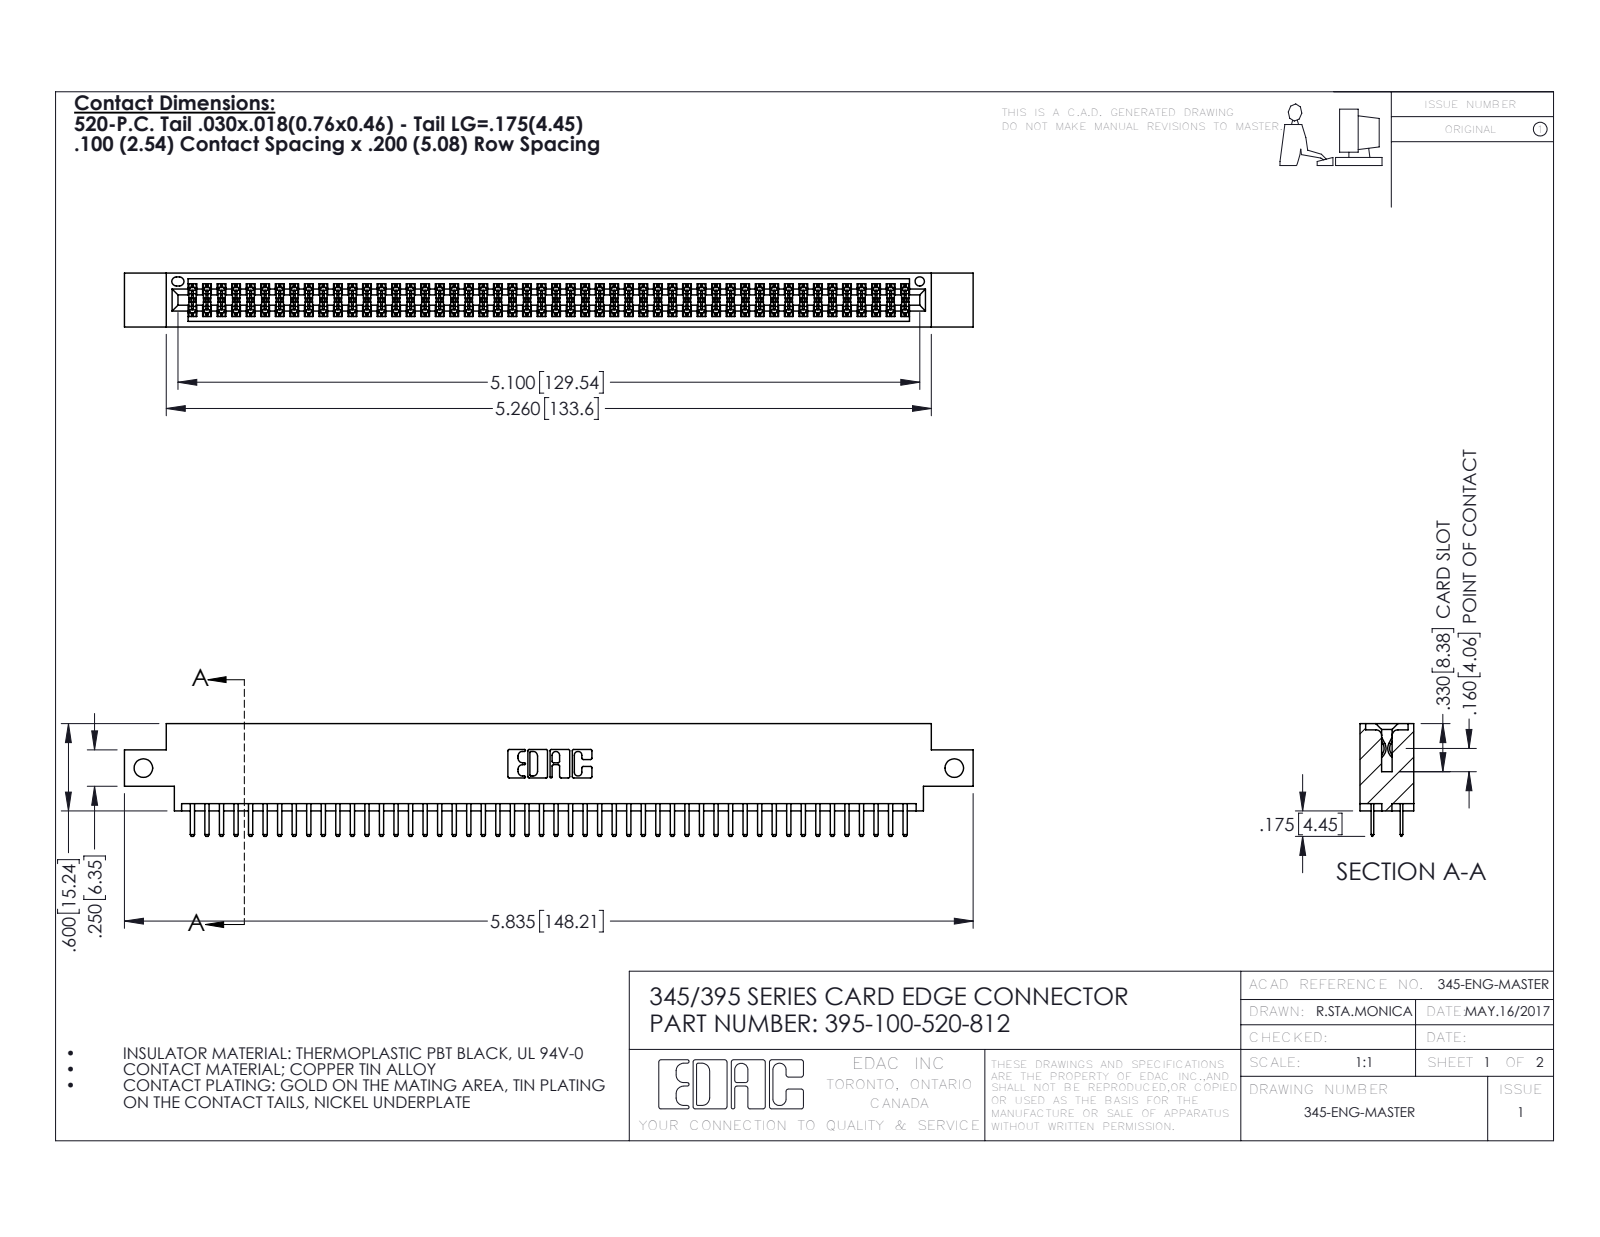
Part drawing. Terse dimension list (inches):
name: 395-100-520-812; 345-292-001_345-293-120; 345 Part_0.170 Offset - Side Mount
written by: SolidWorks 2016 (CONFIG_CONTROL_DESIGN)
unit: in
bodies: 101 solids, 5530 faces (3584 planar, 1946 cylindrical, 0 other)
size: 5.835 × 0.775 × 0.37
volume: 0.868 in³; area: 32.7 in²
holes: 2× ⌀0.128, 1× ⌀0.064
rounds: 150× R0.006, 104× R0.01, 22× R0.01, 6× R0.007, 6× R0.031, 3× R0.026, 2× R0.014, 2× R0.019
face distances: 0.072, 0.298, 0.2, 0.37, 0.098, 0.272, 0.025, 0.225, 0.022, 0.175
hole spacings: 5.575
